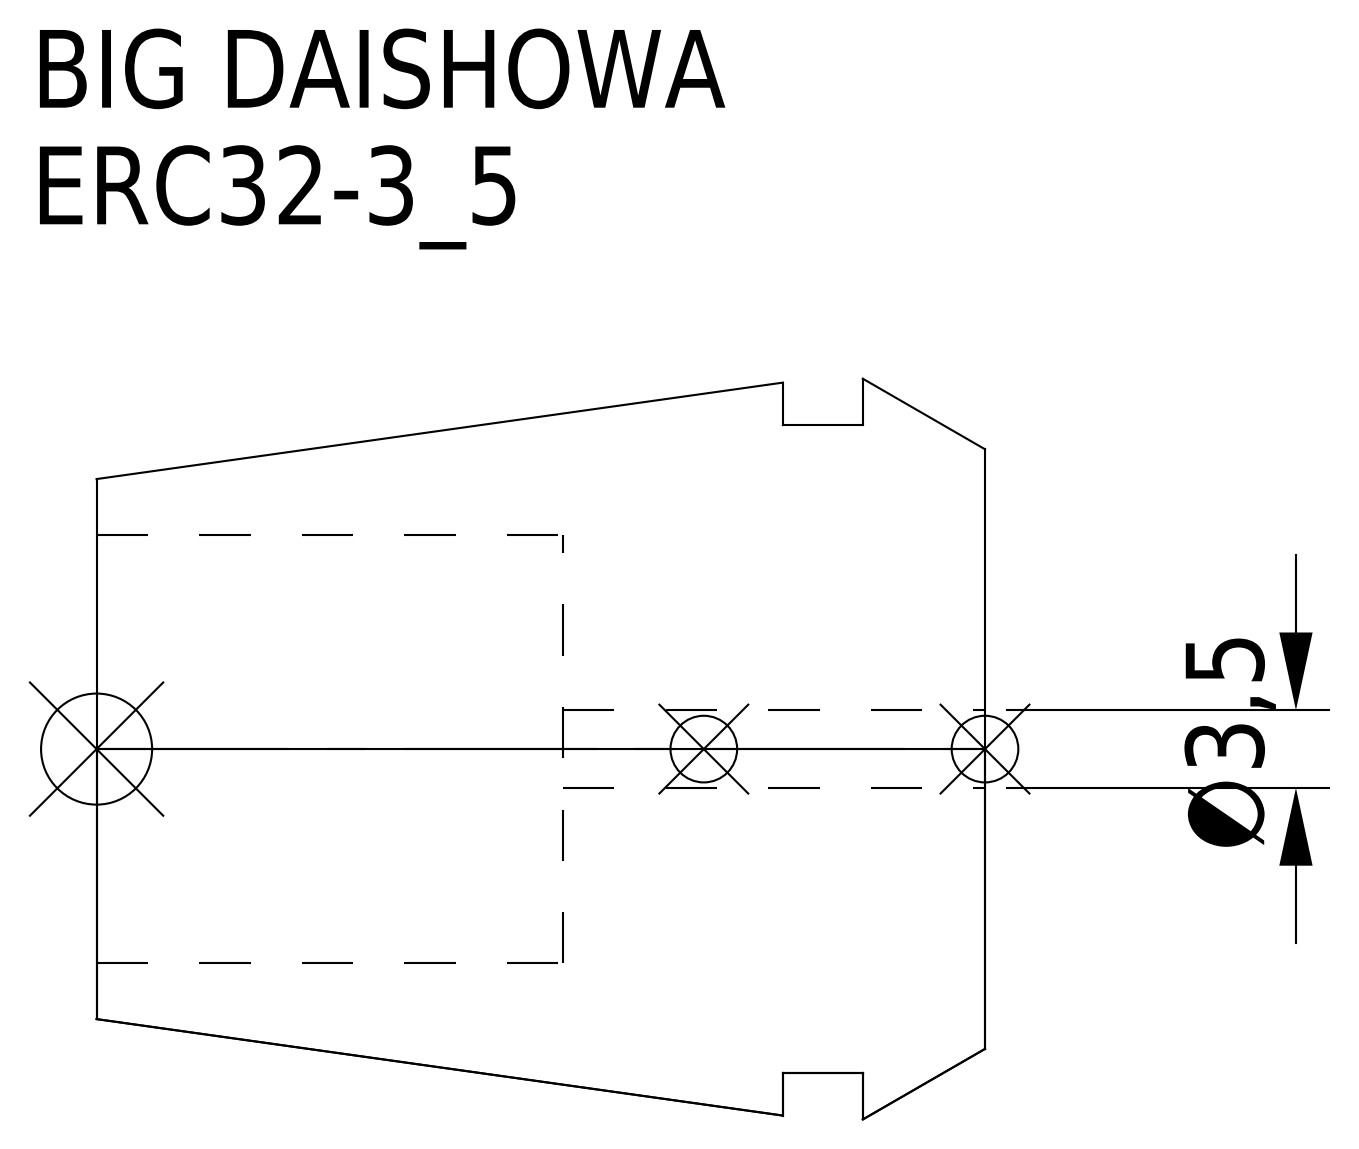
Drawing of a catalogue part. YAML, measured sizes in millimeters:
part_name: "ERC32-3_5"
step_written_by: "CREO PARAMETRIC BY PTC INC, 2016380 (AUTOMOTIVE_DESIGN)"
units: millimeters
bodies: {solids: 1, faces: 15, planar: 5, cylindrical: 6, other: 4}
overall_size: [40, 33.35, 33.35]
volume: 20116
surface_area: 6631
round_holes:
  - {diameter: 3.5, count: 1}
  - {diameter: 19.3, count: 1}
round_bosses_or_shafts:
  - {diameter: 29.2, count: 1}
face_to_face_distances: [19, 5.5, 13.5, 9.1, 3.6, 9.9, 40, 34.5, 30.9, 21]
